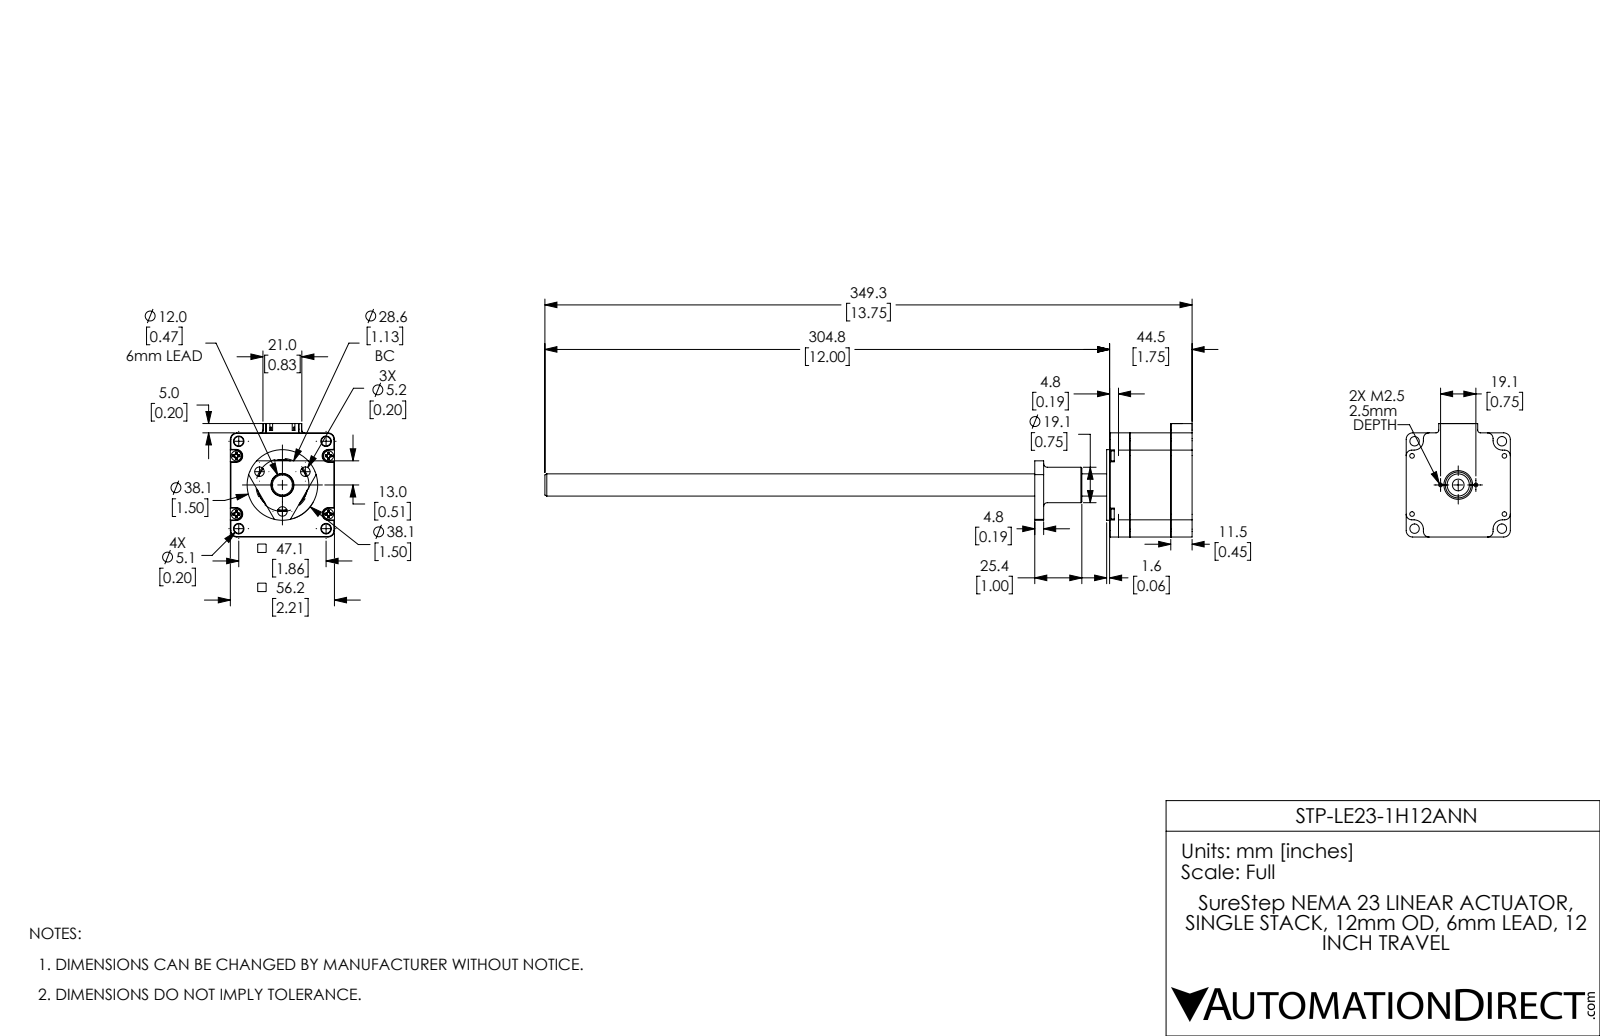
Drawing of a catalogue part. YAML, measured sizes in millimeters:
part_name: "STP-LE23-1H12ANN_2; STP-LE23-1H12ANN_1; STP-LE23-1H12ANN"
step_written_by: "SolidWorks 2017 (AUTOMOTIVE_DESIGN)"
units: millimeters
bodies: {solids: 8, faces: 712, planar: 282, cylindrical: 199, other: 231}
overall_size: [349.3, 61.22, 56.2]
volume: 141407
surface_area: 55898
round_holes:
  - {diameter: 4.5, count: 8}
  - {diameter: 2.5, count: 4}
  - {diameter: 3.3, count: 4}
  - {diameter: 5.1, count: 4}
  - {diameter: 5.16, count: 3}
  - {diameter: 2, count: 2}
  - {diameter: 2.05, count: 2}
  - {diameter: 6.35, count: 1}
  - {diameter: 6.8, count: 1}
  - {diameter: 10.5, count: 1}
  - {diameter: 15.5, count: 1}
  - {diameter: 20, count: 1}
round_bosses_or_shafts:
  - {diameter: 5.4, count: 4}
  - {diameter: 38.1, count: 1}
  - {diameter: 36, count: 1}
  - {diameter: 35.6, count: 1}
  - {diameter: 34.85, count: 1}
  - {diameter: 19.1, count: 1}
  - {diameter: 16, count: 1}
  - {diameter: 12, count: 1}
partial_cylinders:
  - {radius: 1.5, count: 10}
  - {radius: 3, count: 8}
  - {radius: 1.8, count: 4}
  - {radius: 3.2, count: 4}
  - {radius: 3.5, count: 4}
  - {radius: 5, count: 4}
  - {radius: 19.3, count: 1}
face_to_face_distances: [22, 44.5, 56.2, 11.5, 33.5, 1.6, 51.4, 11, 33, 38.8]
hole_center_spacings: [14.12, 24.75, 33.05, 35.01, 45.74, 48.53, 56.99, 6.55]
